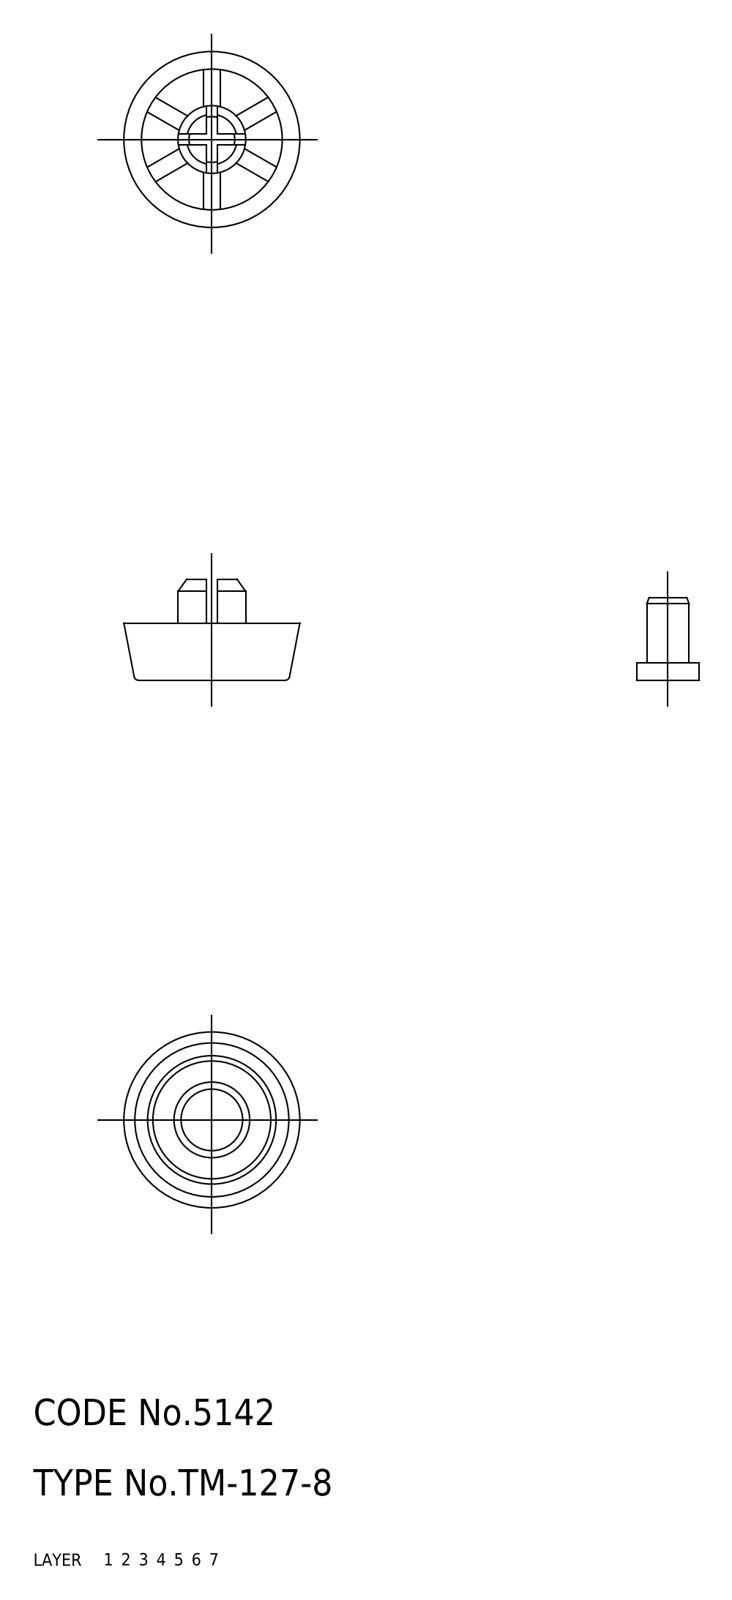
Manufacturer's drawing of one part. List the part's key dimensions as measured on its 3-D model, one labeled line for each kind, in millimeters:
Part name (STEP PRODUCT): 67113616; 67113629
STEP written by: CADfix (AUTOMOTIVE_DESIGN)
Units: millimetres
Bodies: 2 solids, 99 faces (0 planar, 0 cylindrical, 99 other)
Overall size (bounding box): 20 × 20 × 11.5
Volume: 1 545 mm³ · Surface area: 1 762 mm²
